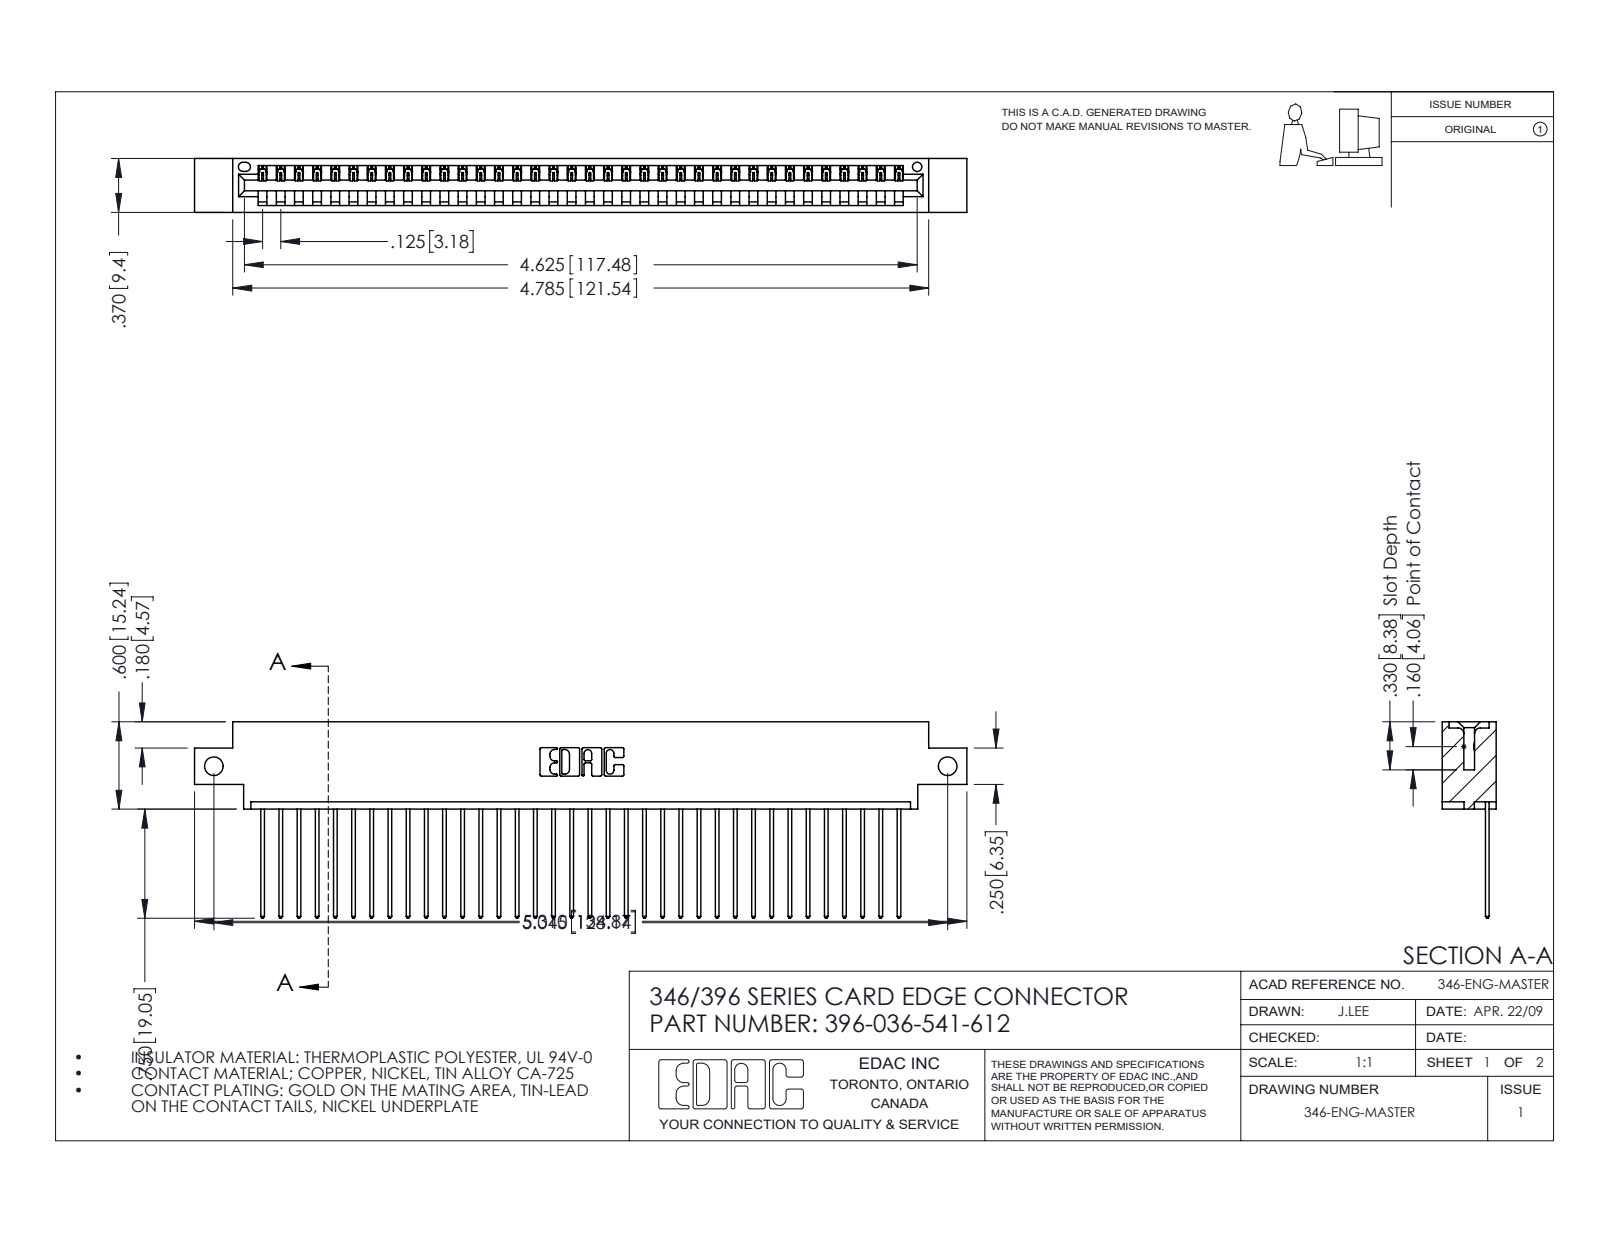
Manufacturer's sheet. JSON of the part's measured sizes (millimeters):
{"part_name": "396-036-541-612; 346 Part_0.170 Offset - Side Mount; 345-292-001_345-293-141", "step_written_by": "SolidWorks 2016 (CONFIG_CONTROL_DESIGN)", "units": "millimeters", "bodies": {"solids": 37, "faces": 2214, "planar": 1520, "cylindrical": 694, "other": 0}, "overall_size": [134.9, 34.3, 9.4], "volume_mm3": 12700, "surface_area_mm2": 16590, "round_holes": [[3.3, 2], [1.6, 1]], "partial_cylinders_radius": [[0.2, 72], [0.3, 72], [0.3, 22], [0.2, 6], [0.8, 6], [0.7, 3], [0.8, 2], [1, 2]], "face_to_face_distances": [1.2, 8.2, 9.4, 6.4, 1.8, 7.6, 0.6, 3.8, 5.6, 2.5], "hole_center_spacings": [128.1]}
